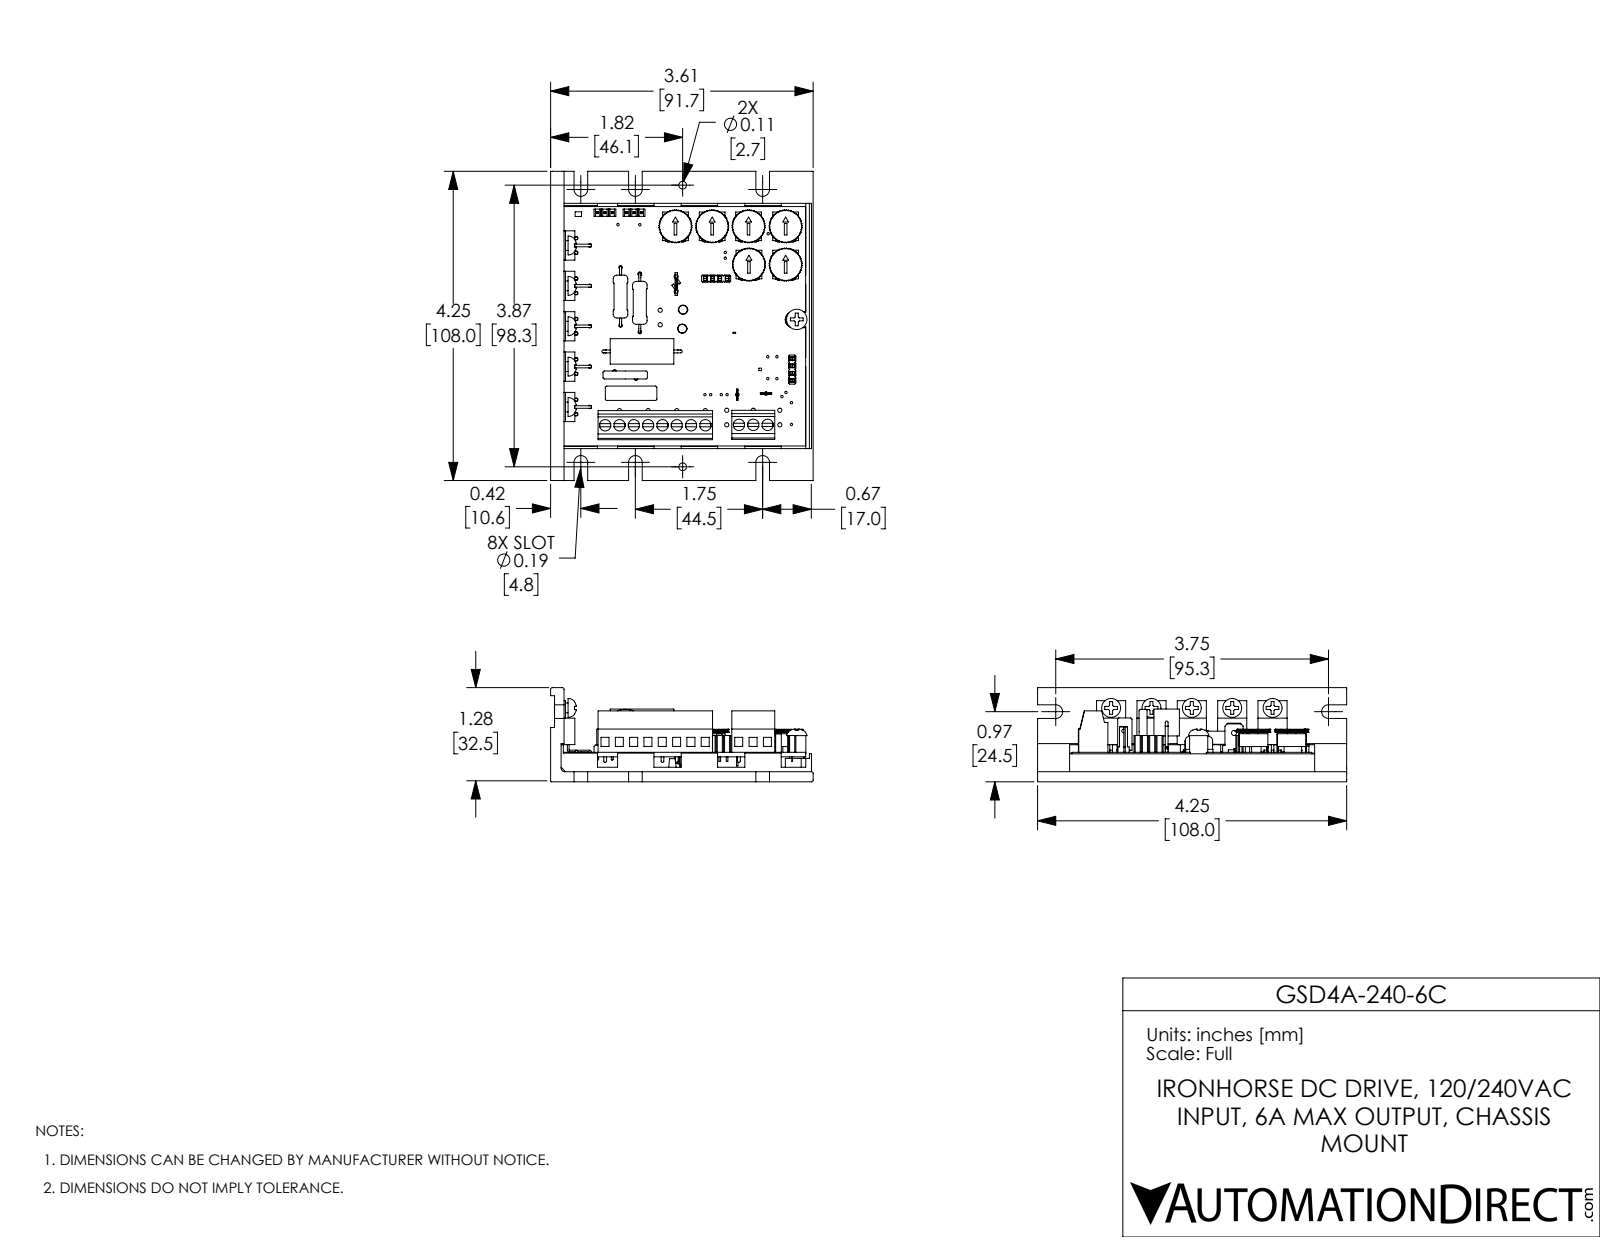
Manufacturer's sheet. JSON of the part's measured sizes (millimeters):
{"part_name": "GSD4A-240-2C b1", "step_written_by": "SolidWorks 2017 (AUTOMOTIVE_DESIGN)", "units": "millimeters", "bodies": {"solids": 51, "faces": 3352, "planar": 2324, "cylindrical": 923, "other": 105}, "overall_size": [108, 91.7, 32.9], "volume_mm3": 88100, "surface_area_mm2": 79290, "round_holes": [[0.8, 35], [1.2, 20], [1.2, 17], [1, 14], [1.5, 13], [4, 11], [1.3, 7], [2.5, 5], [3.7, 5], [1.4, 4], [1.4, 4], [2.7, 3]], "round_bosses_or_shafts": [[1, 13], [1, 7], [3.4, 6], [3, 6], [0.7, 6], [0.8, 4], [5.1, 3], [4.6, 2]], "partial_cylinders_radius": [[0.5, 10], [0.6, 9], [2.4, 8], [1, 6], [5.7, 6], [0.2, 4], [0.5, 4], [1.6, 4]], "face_to_face_distances": [3.6, 10.3, 6.8, 5.2, 8.7, 1.6, 5.1, 3.7, 5.2, 1.5], "hole_center_spacings": [10.3, 5, 7.6, 8.4, 13.3, 15.7, 12.7, 13]}
